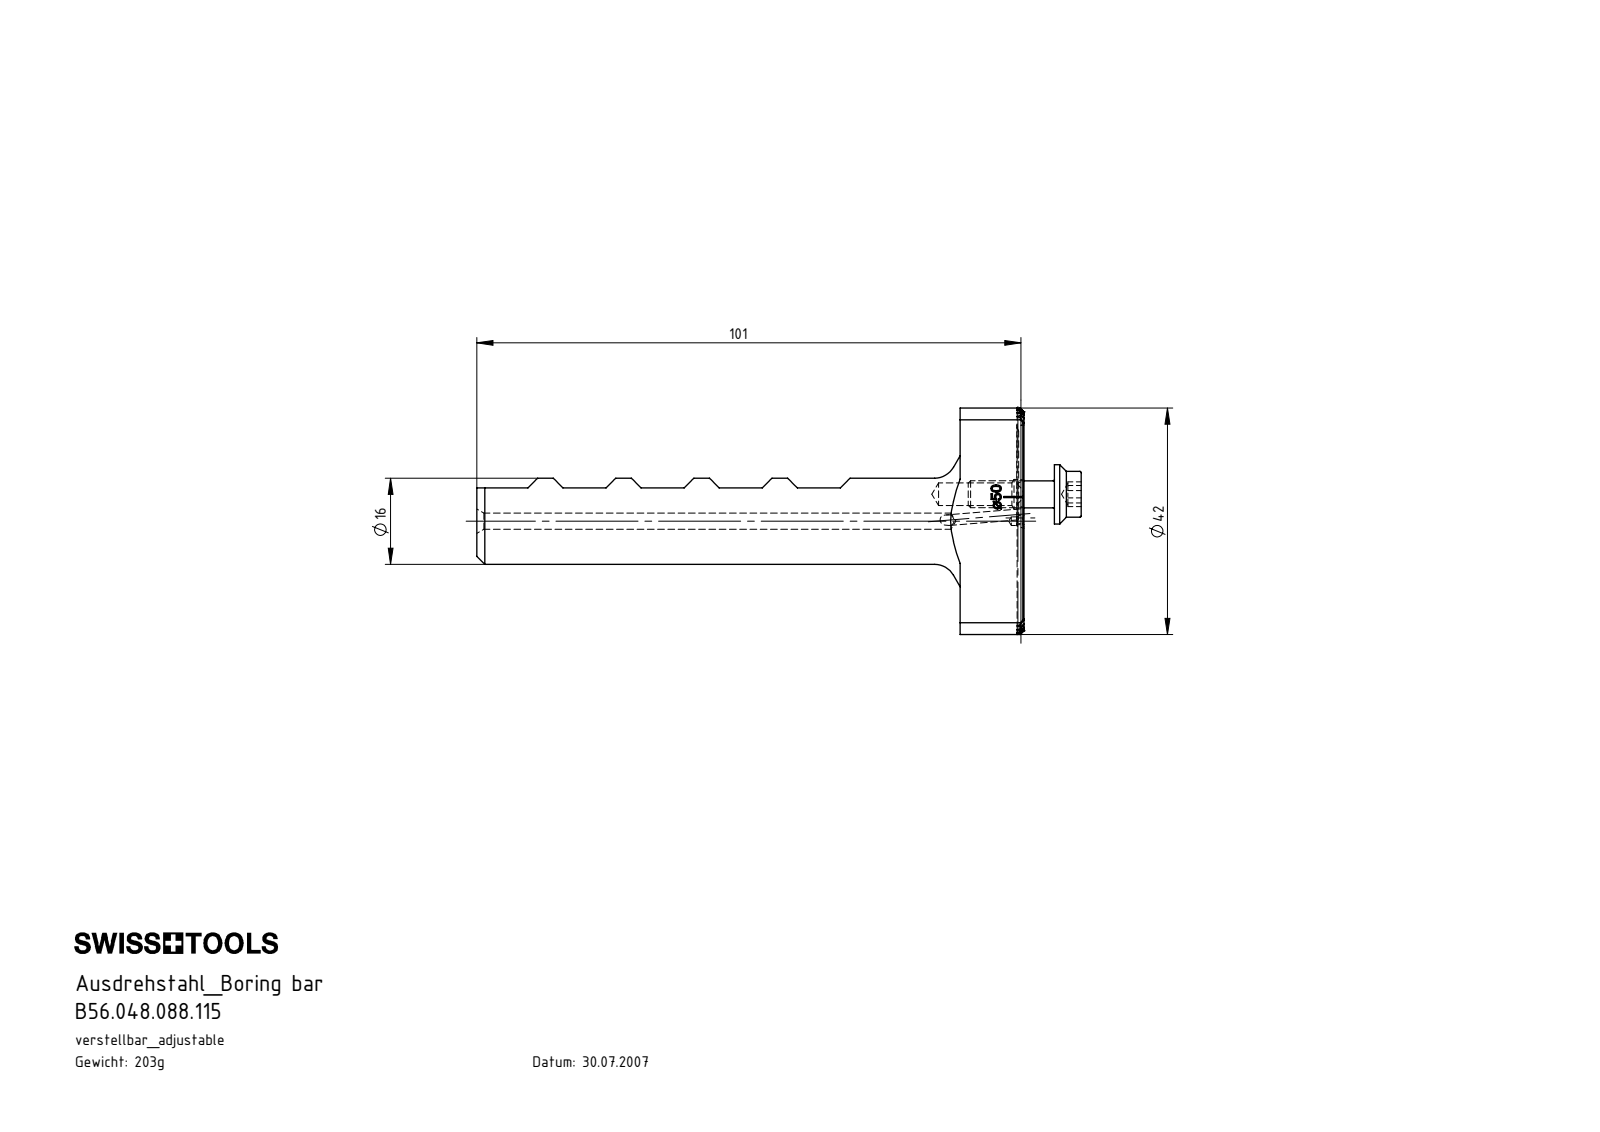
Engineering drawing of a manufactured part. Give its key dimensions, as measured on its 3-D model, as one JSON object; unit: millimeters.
{"part_name": "U16.BV2.K01.101; U16-BV2.K01.101_B; BN 1392 - M5 x 16", "step_written_by": "SolidWorks 2017 (AUTOMOTIVE_DESIGN)", "units": "millimeters", "bodies": {"solids": 2, "faces": 197, "planar": 106, "cylindrical": 28, "other": 63}, "overall_size": [112.2, 42, 18.6], "volume_mm3": 25896, "surface_area_mm2": 9427, "round_holes": [[1.6, 1], [2, 1], [3, 1], [4.2, 1], [5.5, 1]], "round_bosses_or_shafts": [[16, 1], [11, 1], [8.5, 1], [5, 1]], "partial_cylinders_radius": [[0.14, 9], [1.25, 2], [21, 1]], "face_to_face_distances": [1.73, 18.6, 3.46, 8.66, 6.93, 5.2, 3.47, 5.19, 10.39, 1.74], "hole_center_spacings": [5]}
